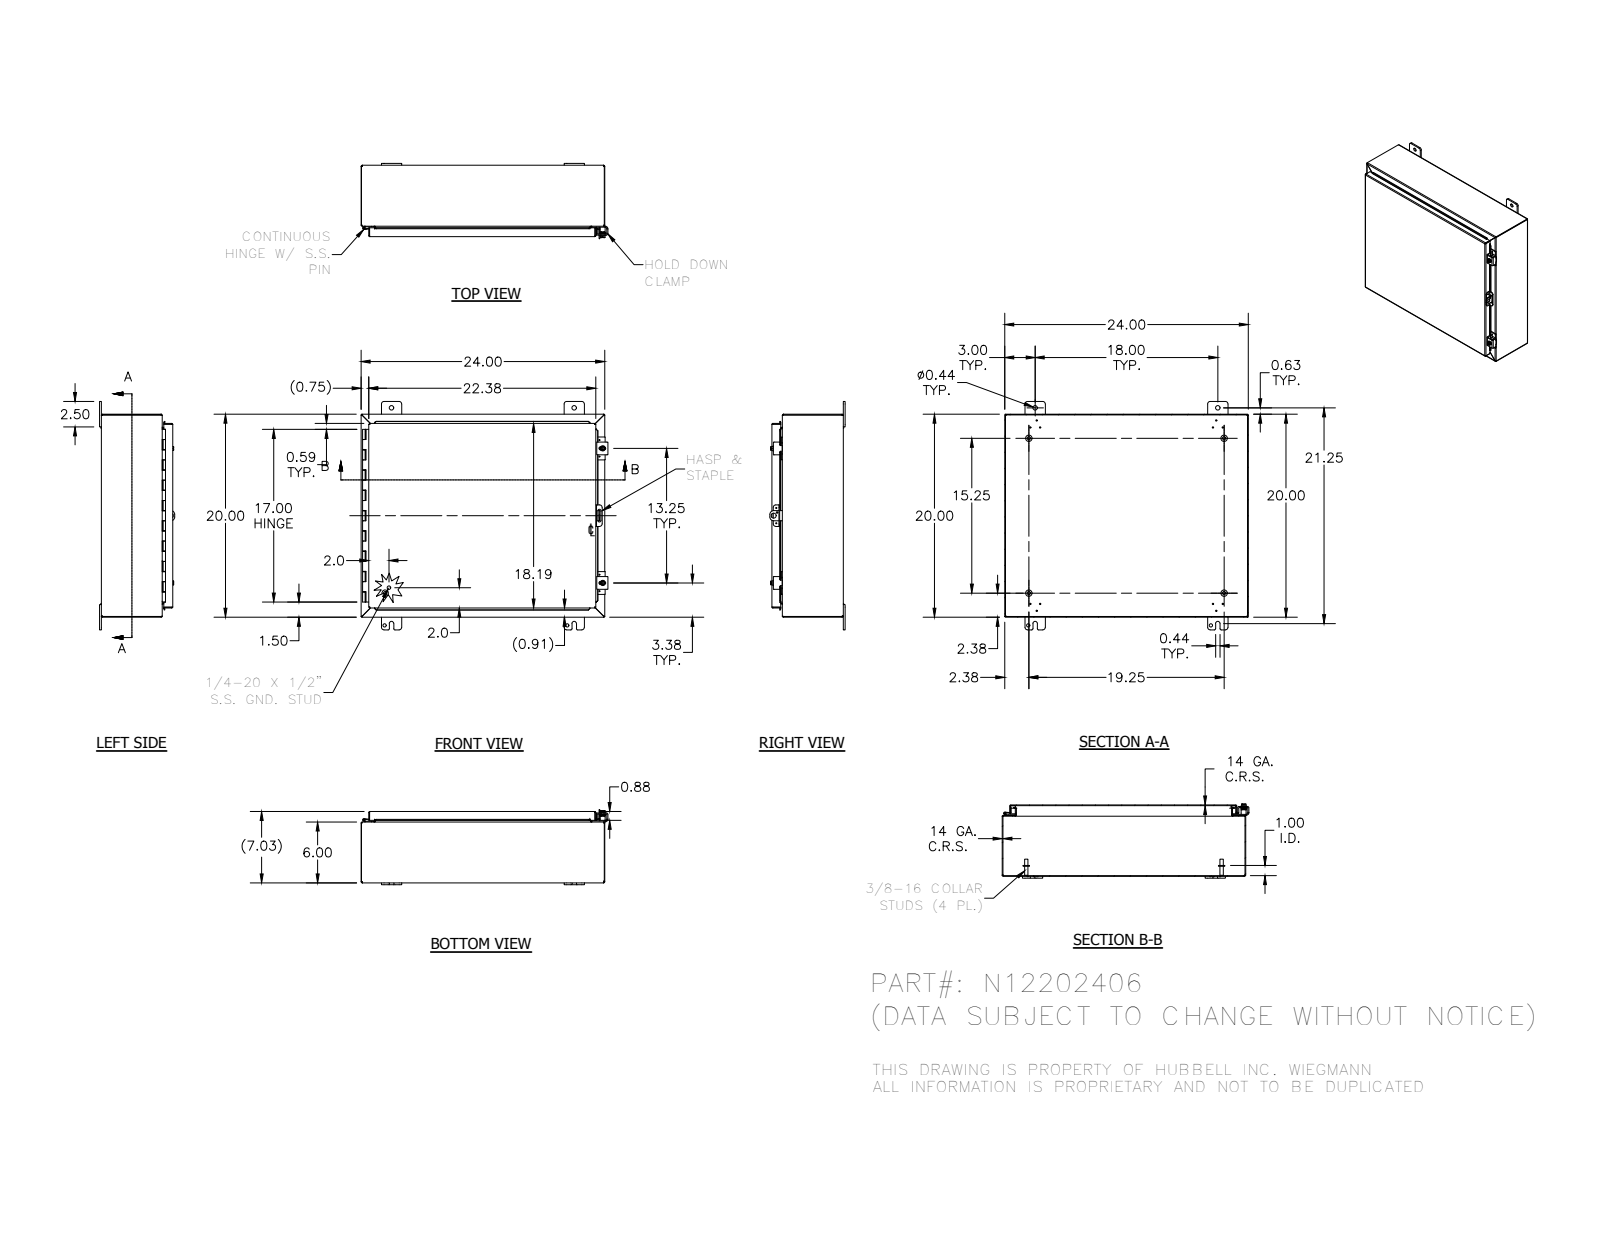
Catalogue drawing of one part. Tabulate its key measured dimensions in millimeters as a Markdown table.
| quantity | value |
| --- | --- |
| part name | N12202406; 34840; 38420; N12202406BKP (+8 more) |
| STEP written by | Autodesk Inventor 2012 (AUTOMOTIVE_DESIGN) |
| units | millimeters |
| bodies | 27 solids, 948 faces (511 planar, 320 cylindrical, 117 other) |
| overall size | 617.5 × 571.5 × 188.2 |
| volume | 2 275 000 mm³ |
| surface area | 2 324 000 mm² |
| round holes (diameter × count) | 3 × 12, 2.8 × 7, 8 × 4, 11.1 × 4, 5.4 × 2, 7.1 × 2, 7.6 × 2, 3.2 × 1, 4 × 1, 12.7 × 1 |
| round bosses / shafts (diameter × count) | 15.9 × 4, 8.4 × 4, 6.4 × 4, 13.2 × 2, 12.7 × 2, 8.9 × 2, 2.9 × 2, 8.6 × 1 |
| partial cylindrical surfaces (radius × count) | 0.8 × 27, 1.6 × 25, 3.2 × 25, 6.4 × 25, 0.8 × 23, 2.7 × 23, 1.8 × 8, 2.5 × 4 |
| main face-to-face distances | 1.9, 176.8, 174.9, 178.6, 506.1, 607.7, 150.5, 26.2, 508, 504.2 |
| hole center spacings | 457.2, 19.3, 21.3, 23.9, 24.6, 40.5, 50.7, 441.2 |
